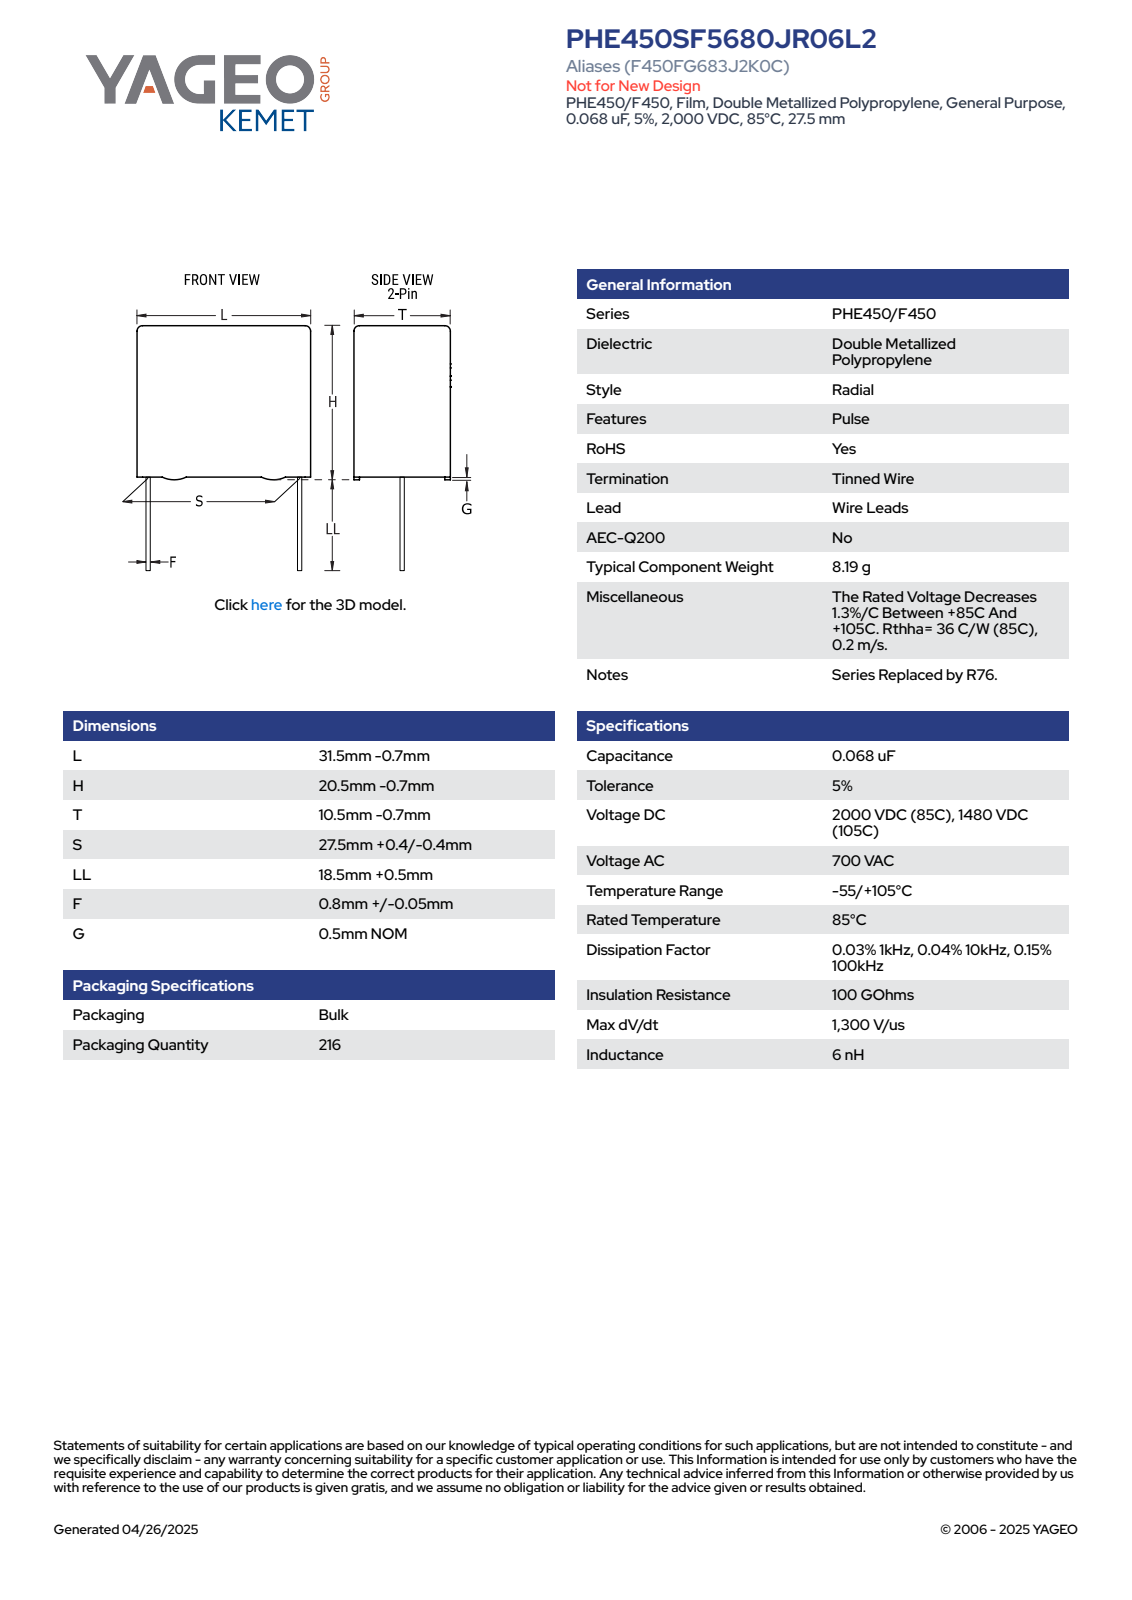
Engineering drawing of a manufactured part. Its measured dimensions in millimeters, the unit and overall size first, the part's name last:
Units: millimetres
Overall size (bounding box): 39.5 × 31.5 × 10.51
Round bosses / shafts (diameter × count): ⌀0.85 ×2
Partial cylindrical surfaces — rounded edges, fillets, slot ends (radius × count): R0.5 ×4
Main face-to-face distances: 10.5, 20, 31.5, 10.51, 0.5, 20.5, 0.6, 9.9, 0.61, 9.3
Volume: 6 639 mm³ · Surface area: 2 556 mm²
Bodies: 4 solids, 89 faces (81 planar, 8 cylindrical, 0 other)
Part name (STEP PRODUCT): CFR_RBG_31.5X20.5X10.5_L31.5H20.5T10.5S27.5LL19F0.85G0.5
STEP written by: SolidWorks 2014 (AUTOMOTIVE_DESIGN)
